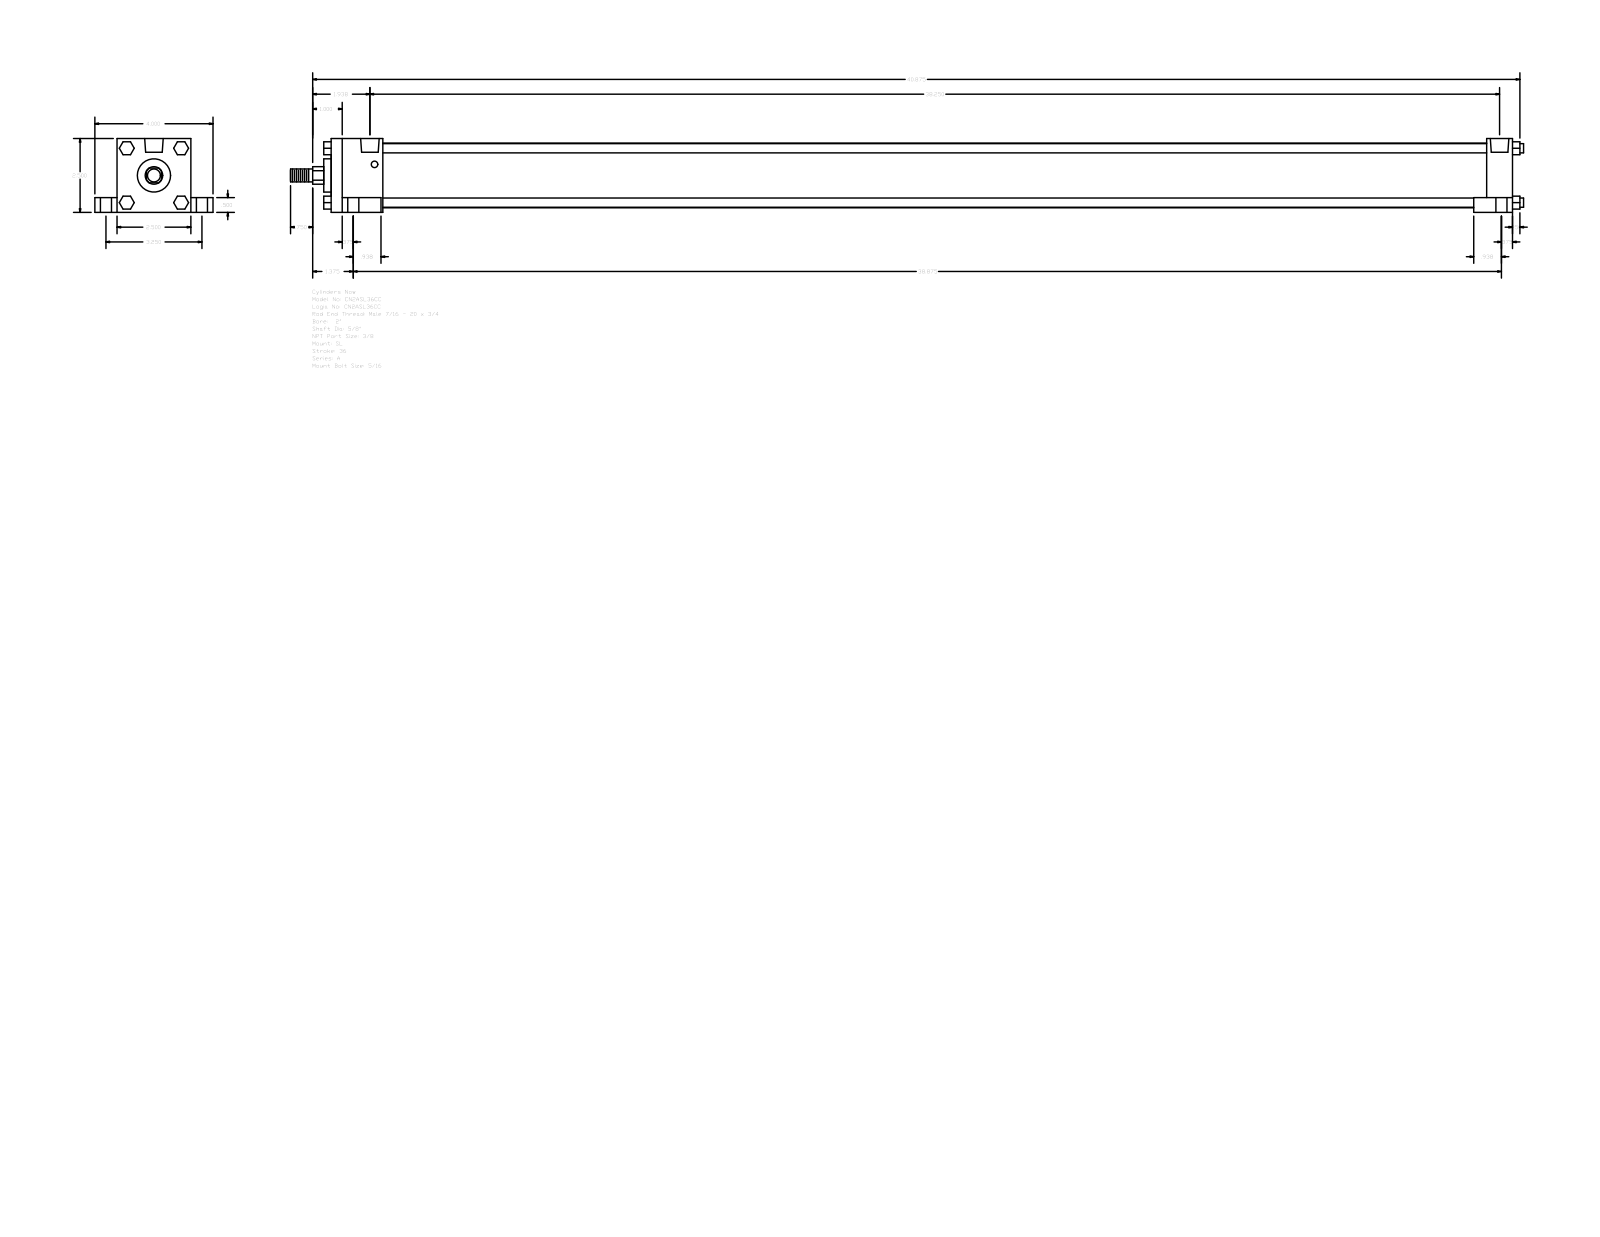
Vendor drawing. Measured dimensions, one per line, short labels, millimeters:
name: A_SL__0200_0.625
written by: GSSL Pune (CONFIG_CONTROL_DESIGN)
unit: mm
bodies: 0 solids, 148 faces (112 planar, 36 cylindrical, 0 other)
size: 1060.45 × 101.6 × 63.5
holes: 4× ⌀5.56, 4× ⌀9.53, 4× ⌀15.88, 2× ⌀15.93
bosses: 4× ⌀7.94, 1× ⌀55.63, 1× ⌀28.57, 1× ⌀15.88, 1× ⌀11.11
rounds: 1× R7.54
face distances: 63.5, 1016, 50.8, 12.7, 19.05, 82.55, 44.45, 971.55, 993.77, 949.32
hole spacings: 41.3, 41.64, 43.67, 45.13, 82.54, 963.6, 970.04, 974.01
